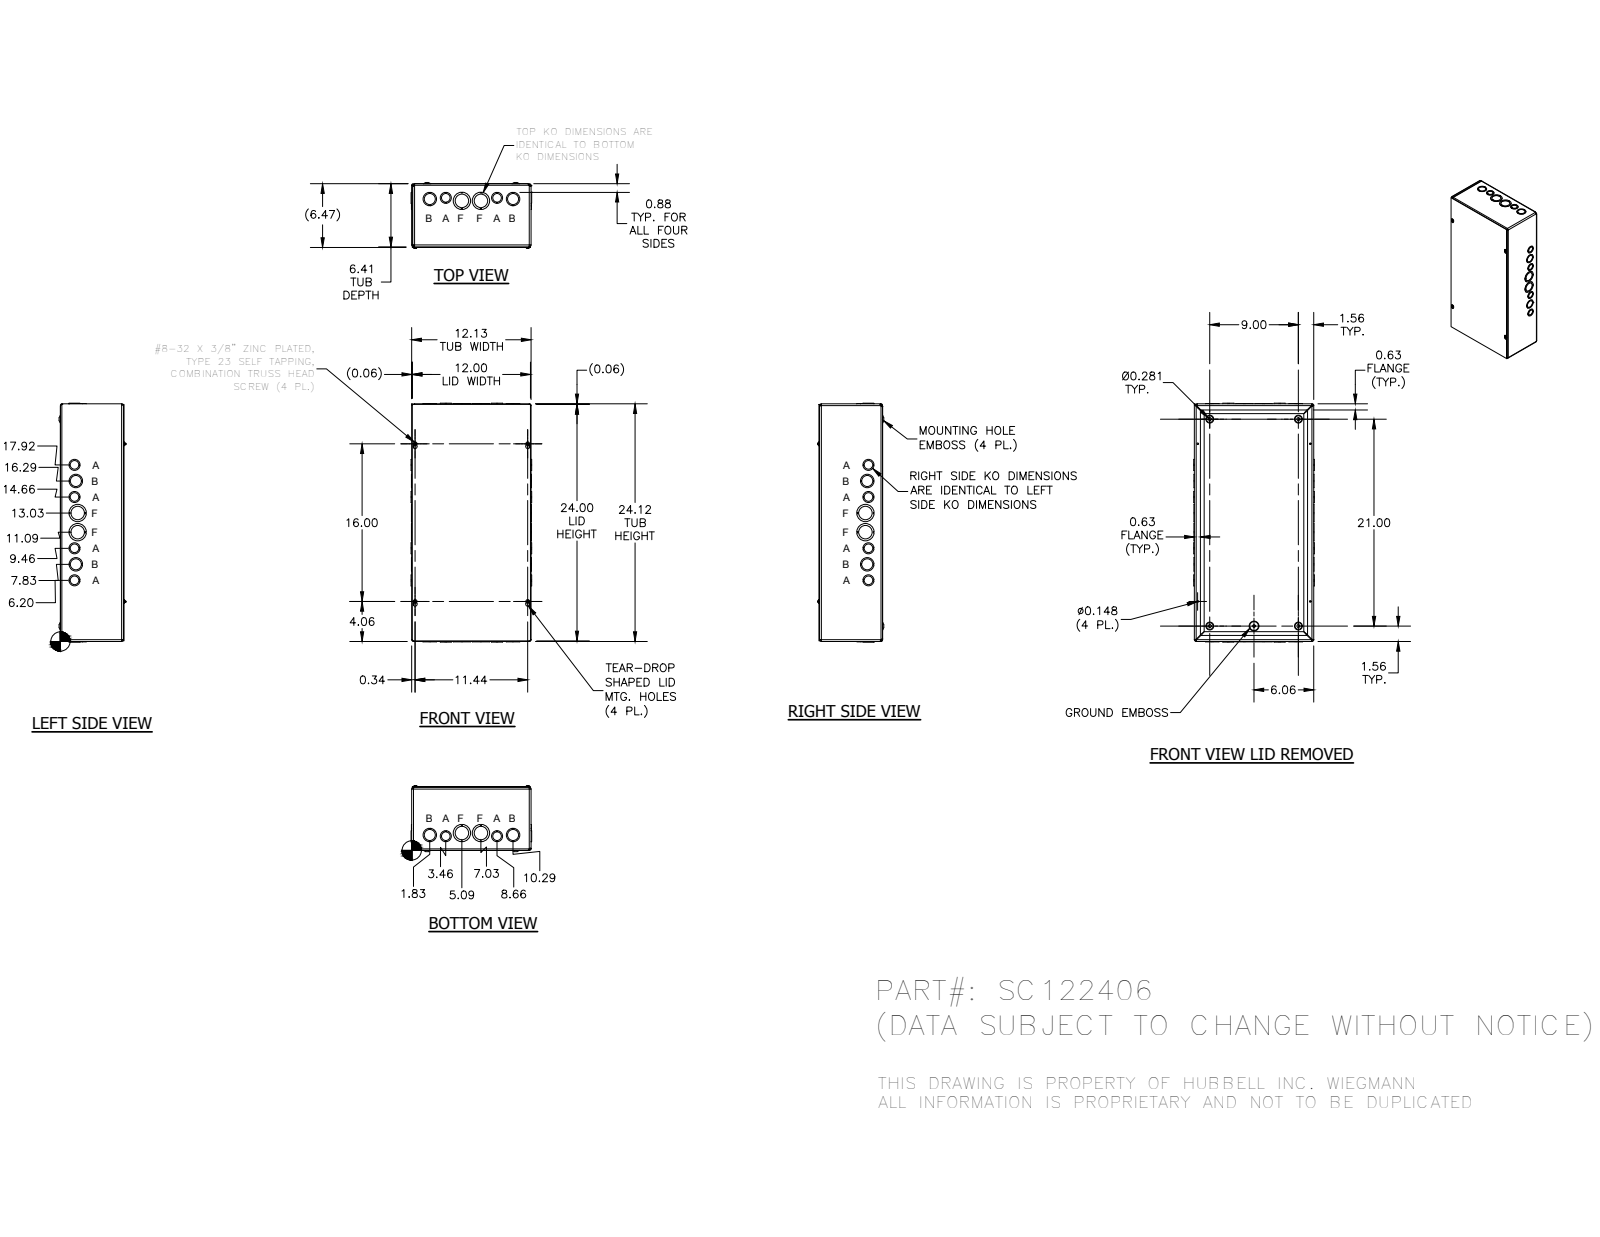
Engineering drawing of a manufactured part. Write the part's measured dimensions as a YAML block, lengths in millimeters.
part_name: "SC1224BKP; SC122406WRA; SC1224LID; 34056 (+1 more)"
step_written_by: "Autodesk Inventor 2014 (AUTOMOTIVE_DESIGN)"
units: millimeters
bodies: {solids: 30, faces: 1142, planar: 749, cylindrical: 235, other: 158}
overall_size: [615.92, 311.12, 170]
round_holes:
  - {diameter: 28.57, count: 10}
  - {diameter: 34.92, count: 8}
  - {diameter: 22.22, count: 6}
  - {diameter: 3.76, count: 4}
  - {diameter: 7.62, count: 4}
  - {diameter: 44.45, count: 4}
  - {diameter: 4.19, count: 1}
round_bosses_or_shafts:
  - {diameter: 9.75, count: 4}
  - {diameter: 4.17, count: 4}
  - {diameter: 5.8, count: 1}
partial_cylinders:
  - {radius: 3.17, count: 12}
  - {radius: 4.75, count: 8}
  - {radius: 1.4, count: 4}
  - {radius: 1.57, count: 4}
  - {radius: 2.38, count: 4}
  - {radius: 2.97, count: 4}
  - {radius: 3.15, count: 4}
  - {radius: 3.96, count: 4}
face_to_face_distances: [1.57, 161.12, 162.69, 1.59, 162.71, 164.28, 1.58, 307.98, 306.4, 306.41]
hole_center_spacings: [41.52, 42.15, 82.94, 91.03, 132.17, 173.51, 470.92, 536.82]
